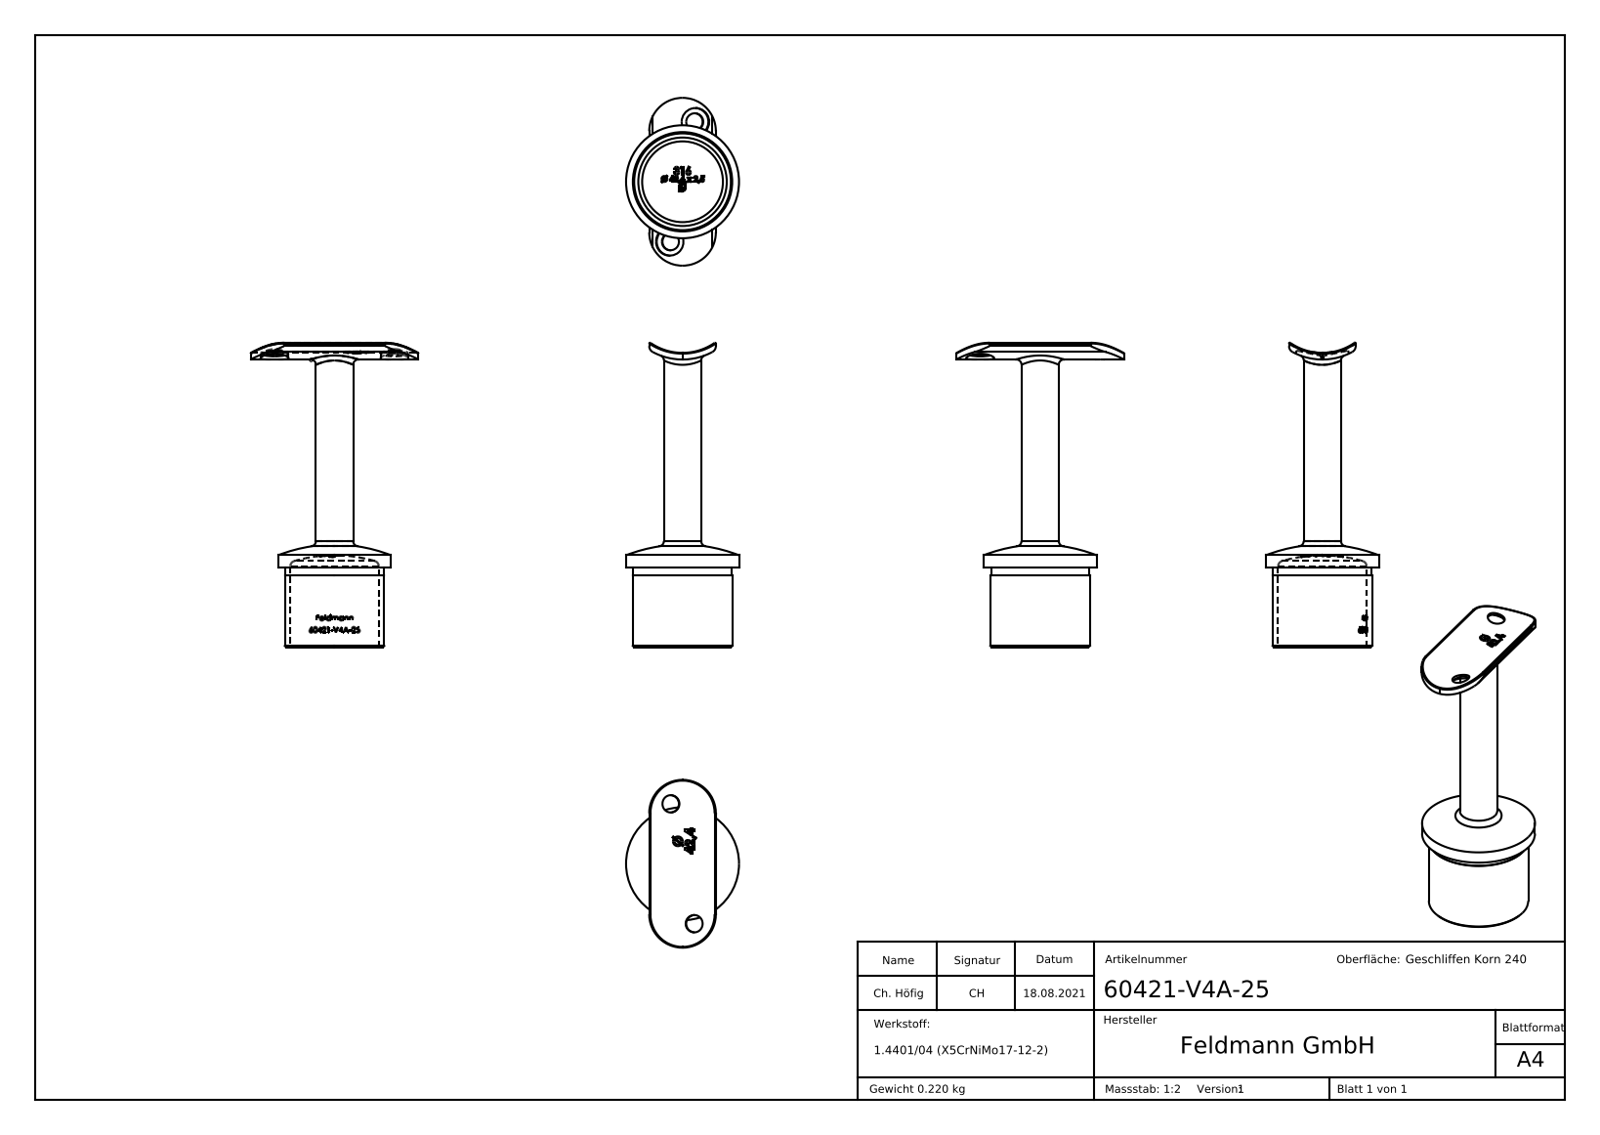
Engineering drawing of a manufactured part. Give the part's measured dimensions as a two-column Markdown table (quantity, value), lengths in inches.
| quantity | value |
| --- | --- |
| part name | 60421-V4A-25 |
| STEP written by | SolidWorks 2018 (CONFIG_CONTROL_DESIGN) |
| units | inches |
| bodies | 1 solid, 559 faces (298 planar, 56 cylindrical, 205 other) |
| overall size | 4.5 × 2.48 × 1.669 |
| volume | 1.675 in³ |
| surface area | 25.54 in² |
| round holes (diameter × count) | 0.256 × 2, 0.413 × 2, 1.307 × 1 |
| round bosses / shafts (diameter × count) | 1.669 × 1, 1.469 × 1, 1.453 × 1, 0.551 × 1 |
| partial cylindrical surfaces (radius × count) | 0.012 × 2, 0.098 × 2, 0.492 × 2, 0.657 × 1, 0.835 × 1, 0.839 × 1, 0.933 × 1 |
| main face-to-face distances | 1.181, 0.984, 0.118, 1.063, 0.023, 0.017, 0.049, 0.087, 0.669, 0.178 |
